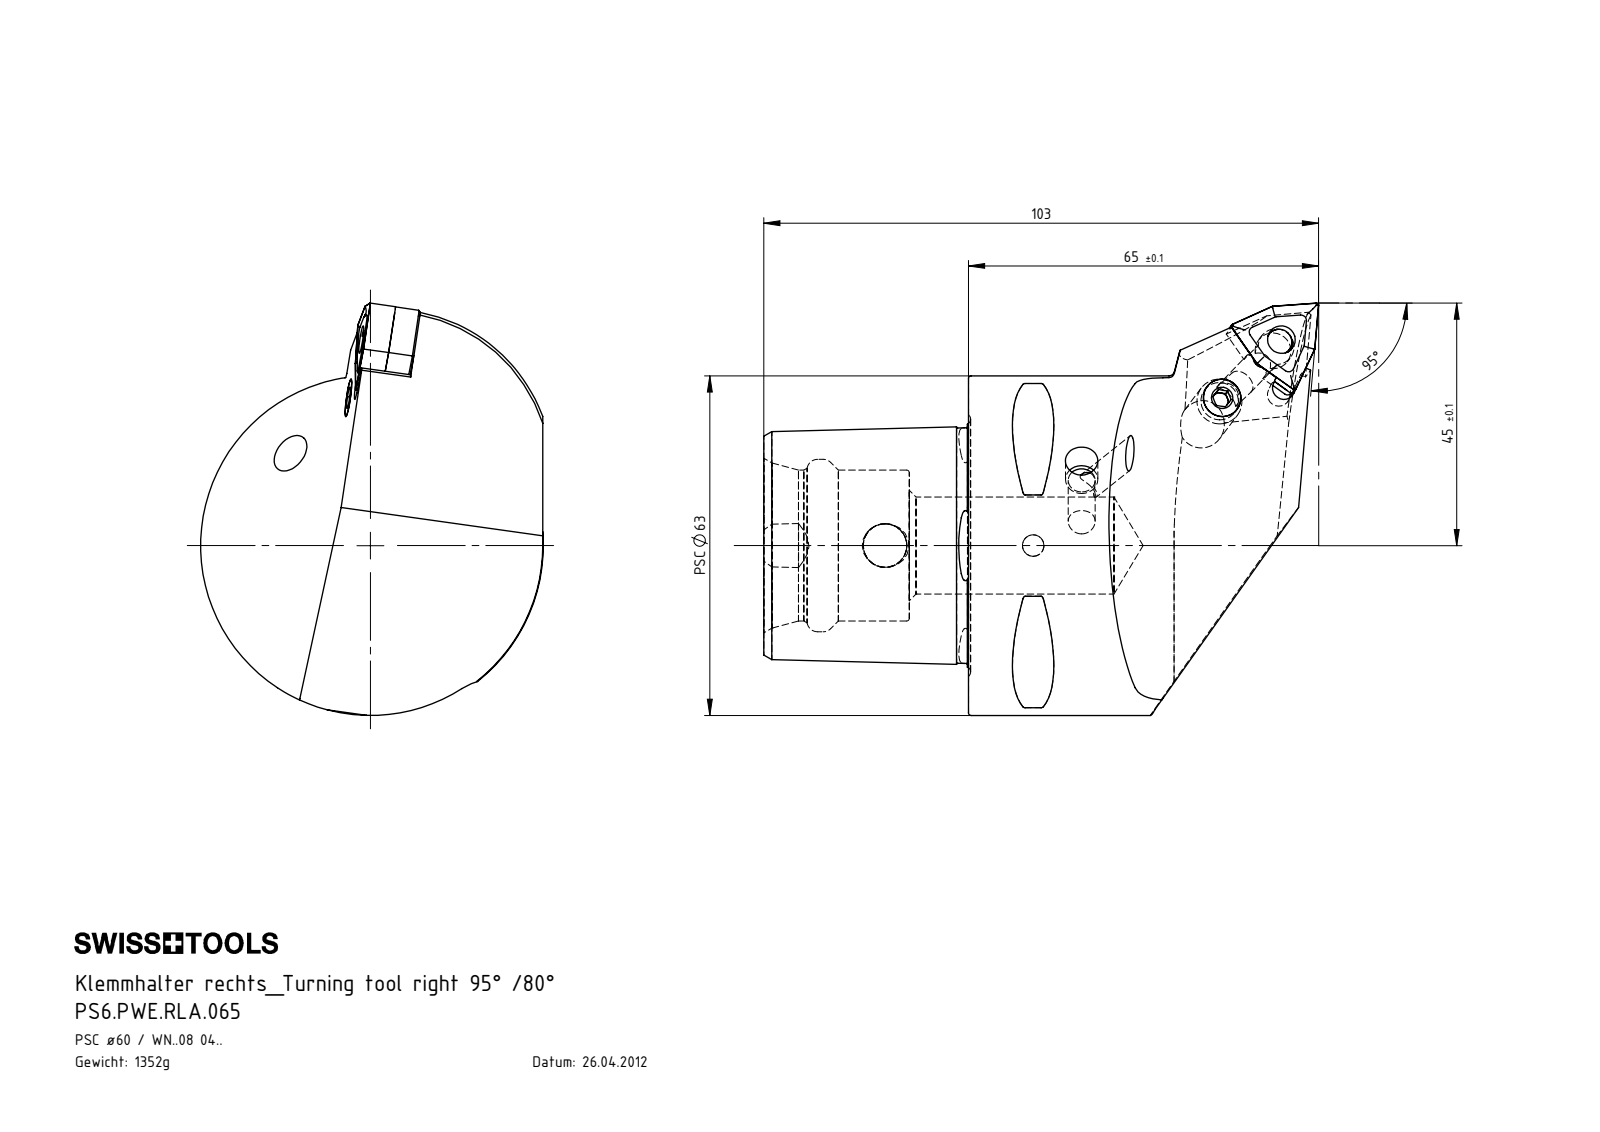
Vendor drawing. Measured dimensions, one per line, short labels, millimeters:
name: PS6-PWE.RLA.065_A; WNMG080404; WWE-ER2.101.004_A; PS6-PWE.RLA.065 (+4 more)
written by: SolidWorks 2012 (CONFIG_CONTROL_DESIGN)
unit: mm
bodies: 10 solids, 388 faces (105 planar, 89 cylindrical, 194 other)
size: 103 × 76.5 × 63.61
volume: 171 707 mm³; area: 31 744 mm²
holes: 3× ⌀5, 1× ⌀4, 1× ⌀5.16, 1× ⌀6.7, 1× ⌀7, 1× ⌀7.8, 1× ⌀8.1, 1× ⌀8.4, 1× ⌀18, 1× ⌀28, 1× ⌀32
bosses: 2× ⌀6, 1× ⌀63, 1× ⌀8, 1× ⌀7.9, 1× ⌀6.4, 1× ⌀4.7, 1× ⌀3.55
rounds: 8× R0.5, 3× R0.4, 3× R1, 3× R2.5, 2× R6, 1× R2.1, 1× R2.3, 1× R2.35
face distances: 38, 24.88, 4.76, 4.51, 27, 11, 9.27, 55.8, 37.8, 10.8
hole spacings: 15.6, 27.5
